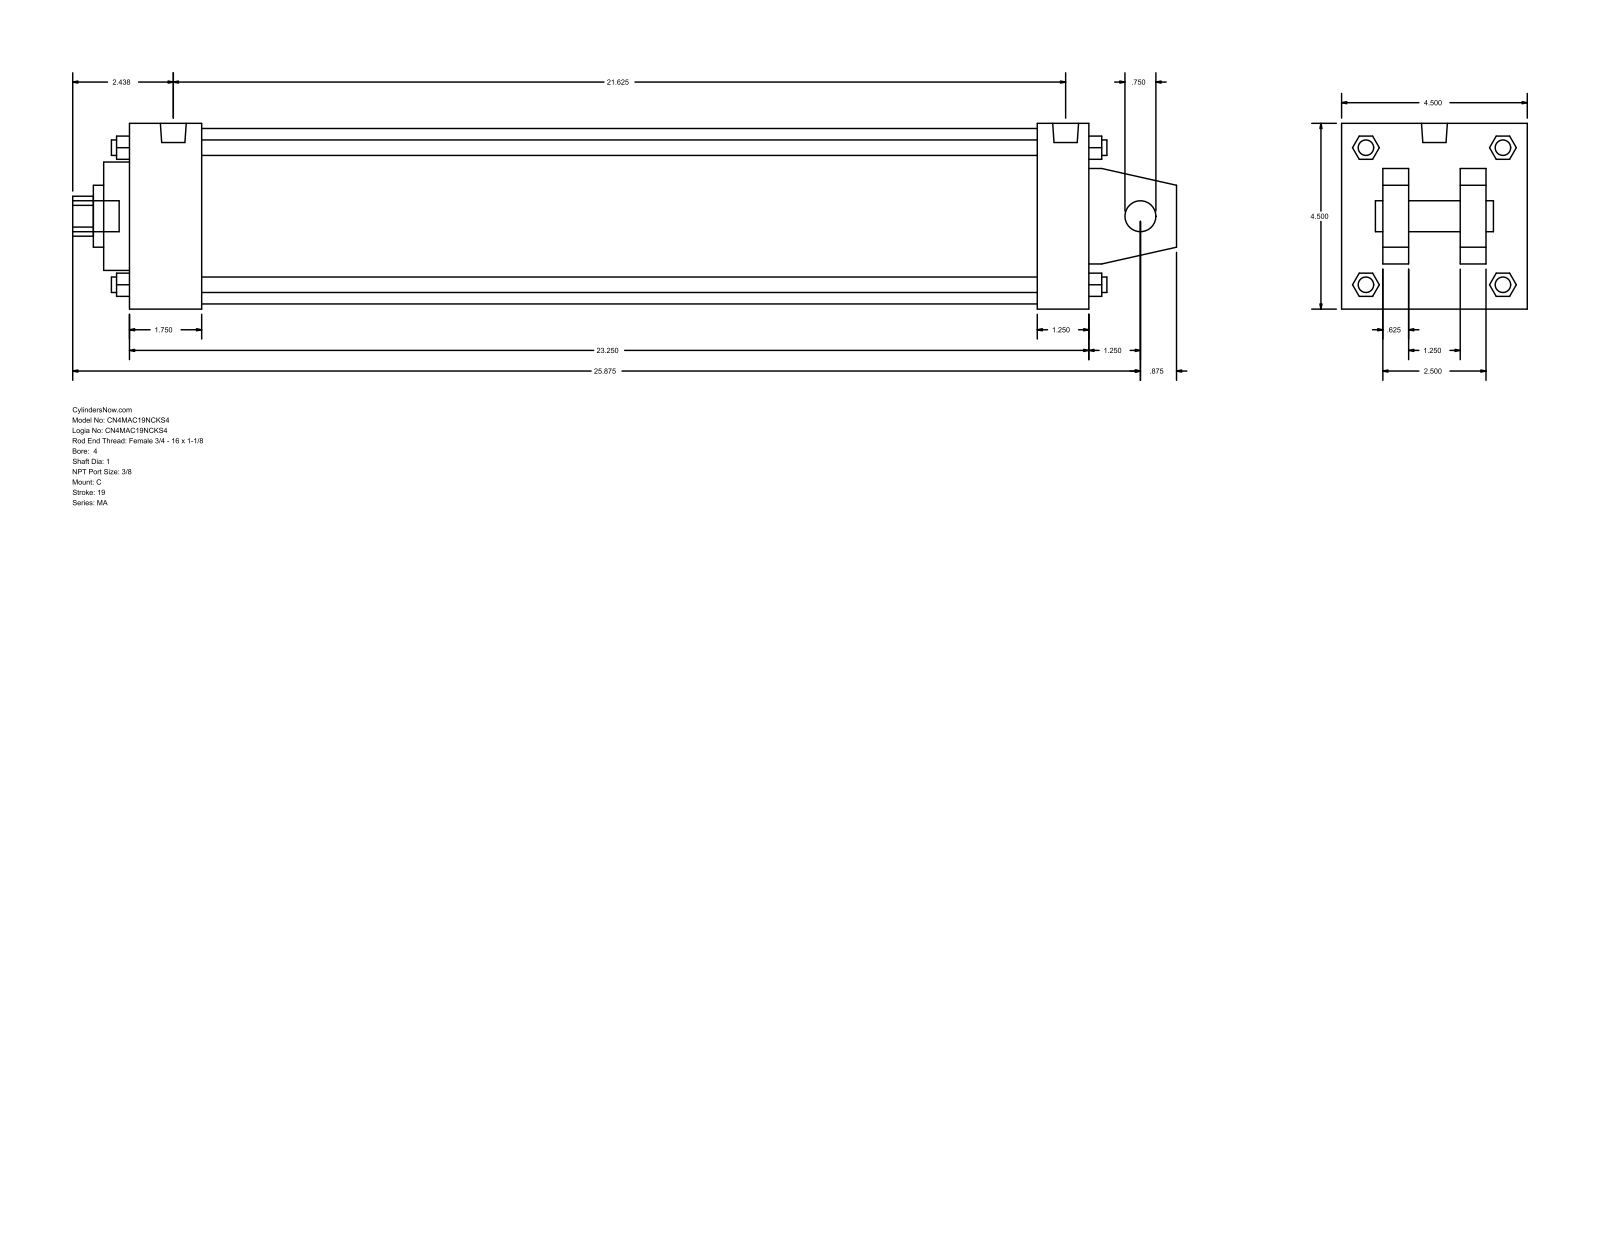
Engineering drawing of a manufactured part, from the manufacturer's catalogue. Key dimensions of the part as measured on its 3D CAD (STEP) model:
Part name (STEP PRODUCT): MA_C__0400_1
STEP written by: GSSL Pune (CONFIG_CONTROL_DESIGN)
Units: millimetres
Bodies: 0 solids, 141 faces (109 planar, 32 cylindrical, 0 other)
Overall size (bounding box): 679.45 × 114.3 × 114.3
Round holes (diameter × count): ⌀19.05 ×1, ⌀25.4 ×1, ⌀38.1 ×1, ⌀66.67 ×1, ⌀107.95 ×1
Round bosses / shafts (diameter × count): ⌀11.11 ×4, ⌀9.53 ×4, ⌀15.93 ×2, ⌀19.05 ×1
Partial cylindrical surfaces — rounded edges, fillets, slot ends (radius × count): R12.29 ×1
Main face-to-face distances: 114.3, 590.56, 15.87, 73.03, 41.27, 25.4, 88.9, 47.63, 558.81, 31.75
